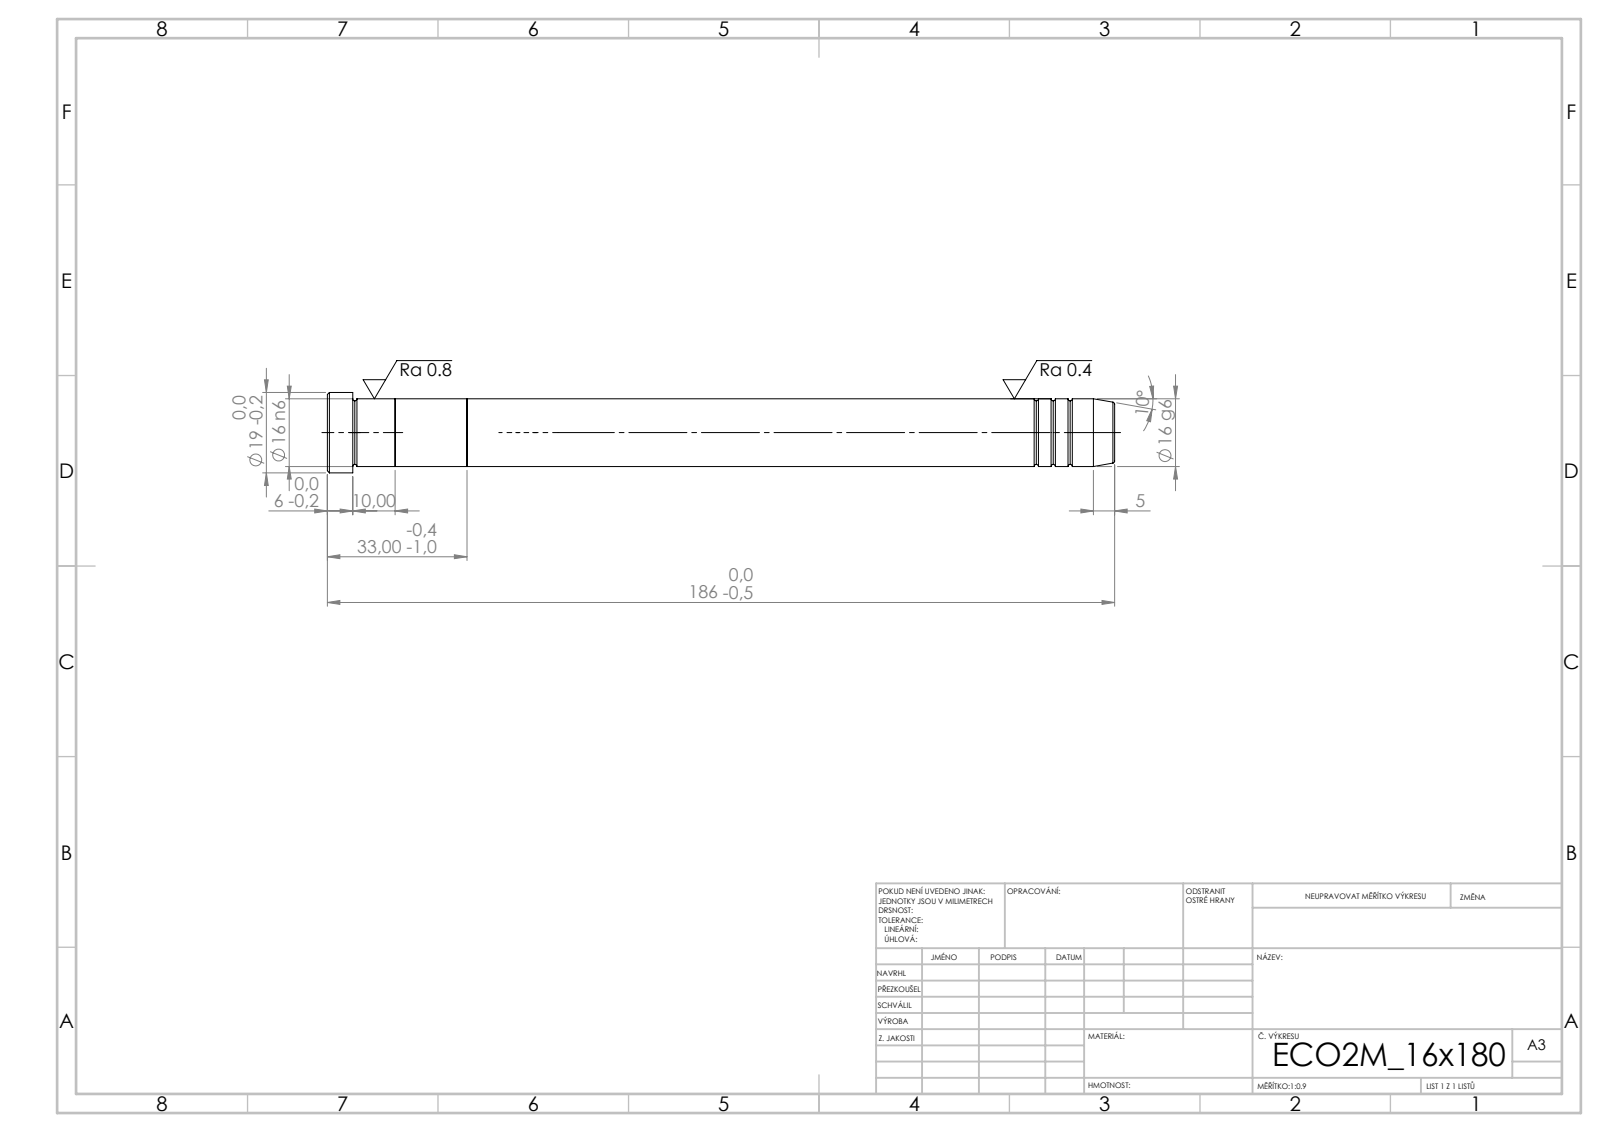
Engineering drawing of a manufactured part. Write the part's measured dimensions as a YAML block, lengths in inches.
step_written_by: "SolidWorks 2019 (CONFIG_CONTROL_DESIGN)"
units: inches
bodies: {solids: 3, faces: 43, planar: 7, cylindrical: 14, other: 22}
overall_size: [7.323, 0.748, 0.748]
volume: 2.301
surface_area: 16.74
round_bosses_or_shafts:
  - {diameter: 0.748, count: 1}
  - {diameter: 0.63, count: 1}
face_to_face_distances: [0.669, 1.299, 0.63, 6.024, 6.693, 7.323, 7.087, 1.063, 0.394, 0.236]
